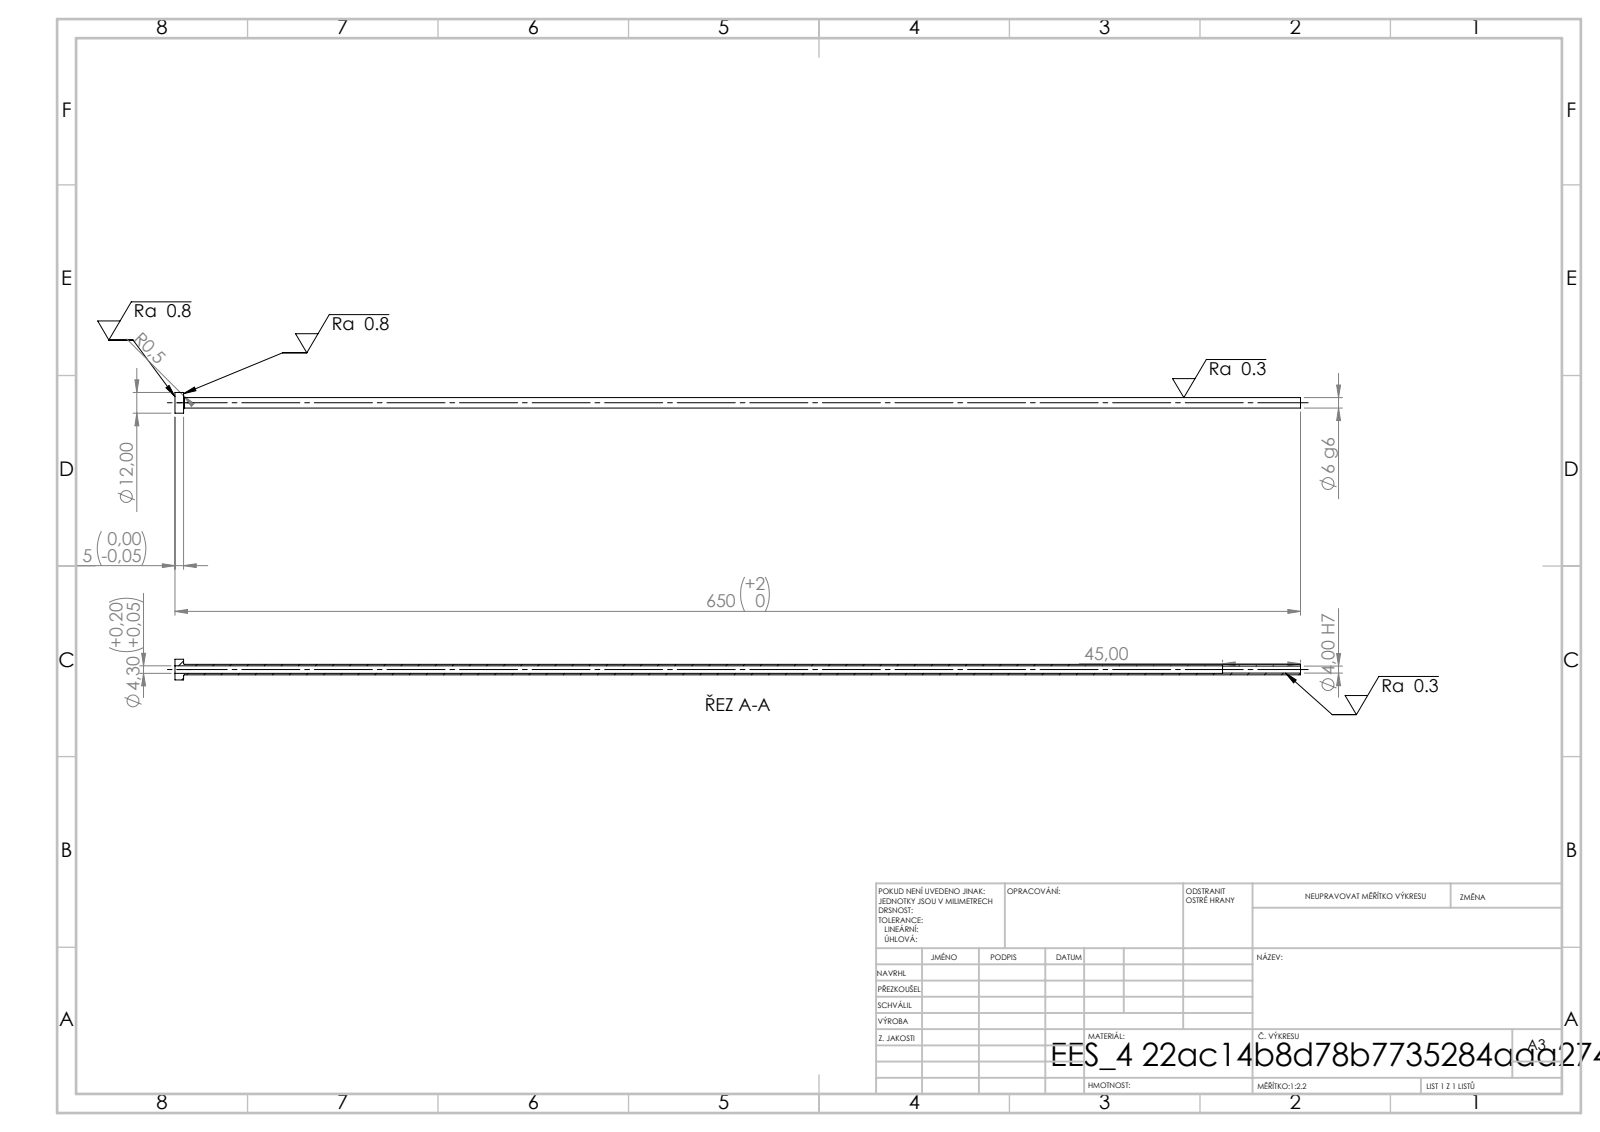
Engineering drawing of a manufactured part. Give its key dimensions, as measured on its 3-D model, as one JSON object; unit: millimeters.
{"step_written_by": "SolidWorks 2019 (CONFIG_CONTROL_DESIGN)", "units": "millimeters", "bodies": {"solids": 1, "faces": 14, "planar": 4, "cylindrical": 8, "other": 2}, "overall_size": [650, 12, 12], "volume_mm3": 9452, "surface_area_mm2": 21282, "round_holes": [[4, 1], [4.3, 1]], "round_bosses_or_shafts": [[12, 1], [6, 1]], "face_to_face_distances": [5, 650, 645, 605, 600, 45]}
